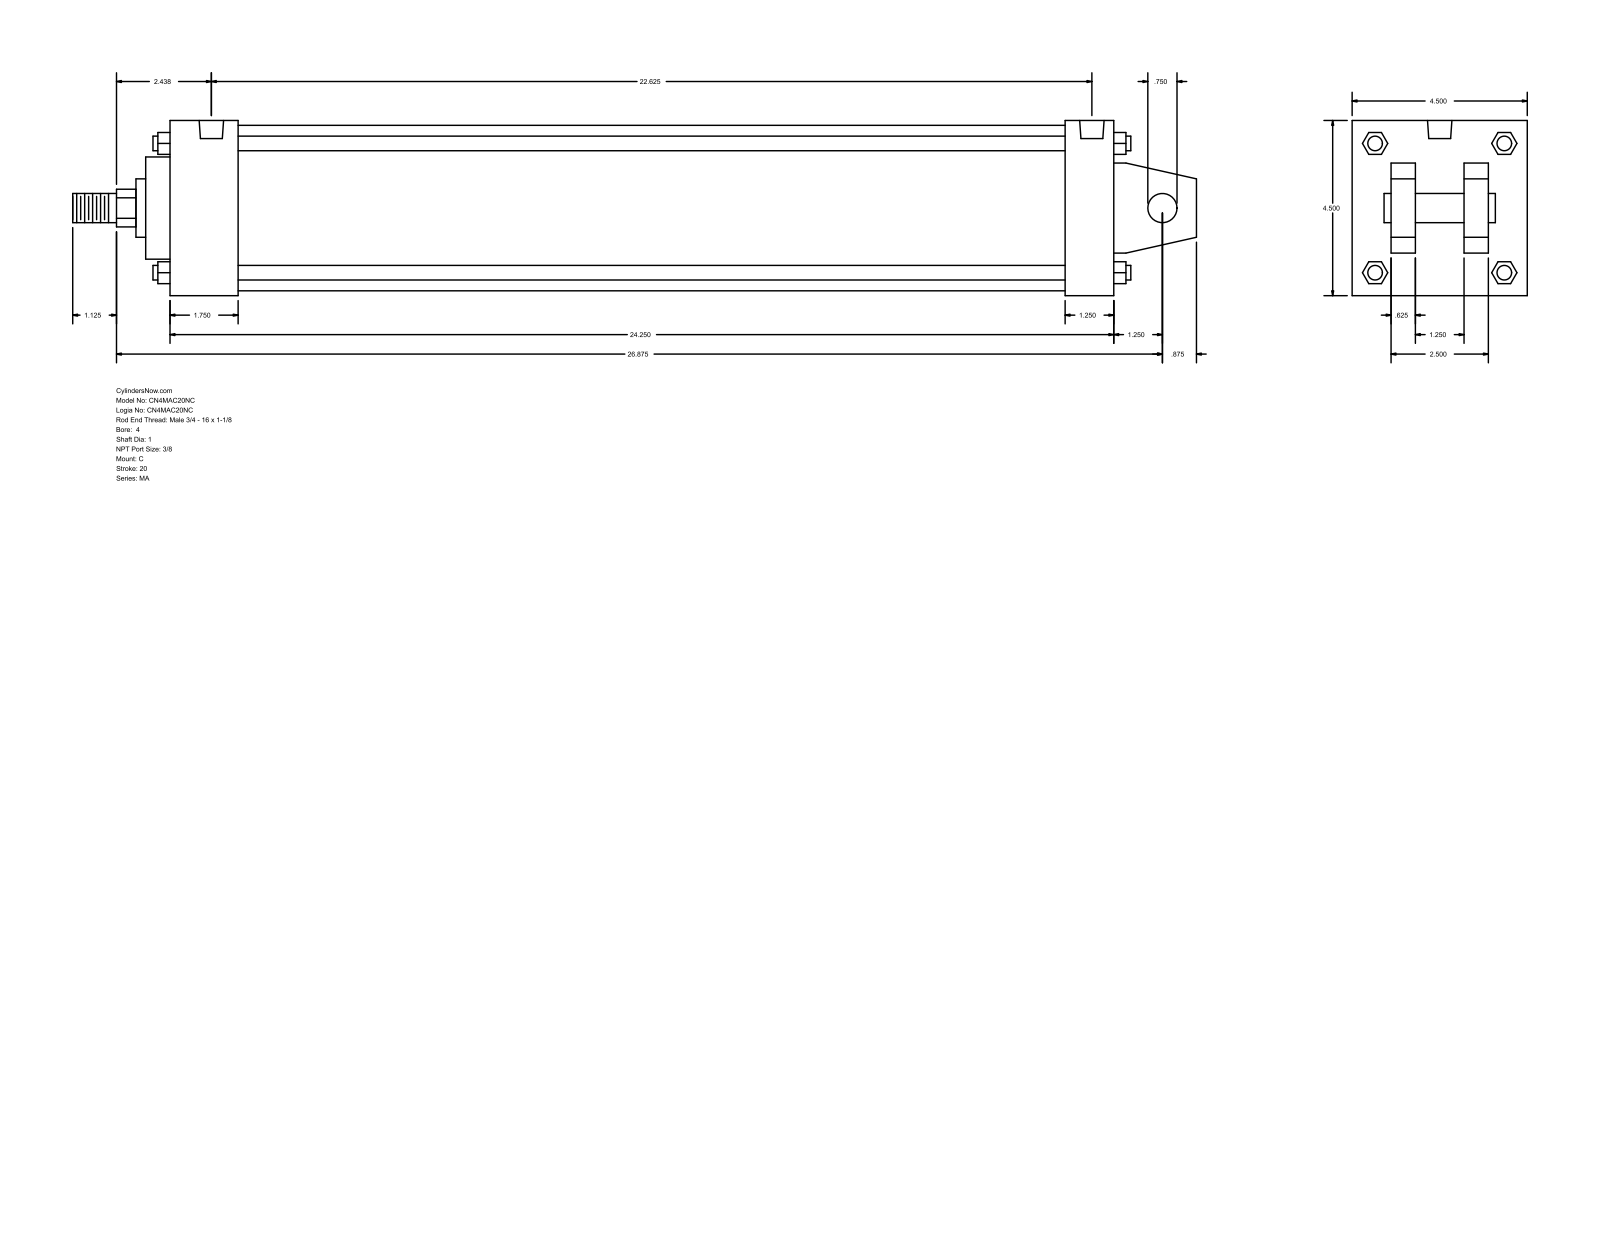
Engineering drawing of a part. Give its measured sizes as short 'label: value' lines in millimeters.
name: MA_C__0400_1
written by: GSSL Pune (CONFIG_CONTROL_DESIGN)
unit: mm
bodies: 0 solids, 141 faces (109 planar, 32 cylindrical, 0 other)
size: 733.42 × 114.3 × 114.3
holes: 4× ⌀11.11, 2× ⌀15.93
bosses: 4× ⌀9.53, 2× ⌀19.05, 1× ⌀107.95, 1× ⌀66.67, 1× ⌀38.1, 1× ⌀25.4
rounds: 1× R12.29
face distances: 114.3, 615.96, 15.87, 31.76, 73.03, 41.27, 25.4, 88.9, 47.63, 584.2
hole spacings: 4.76, 565.16, 569.92, 574.68
